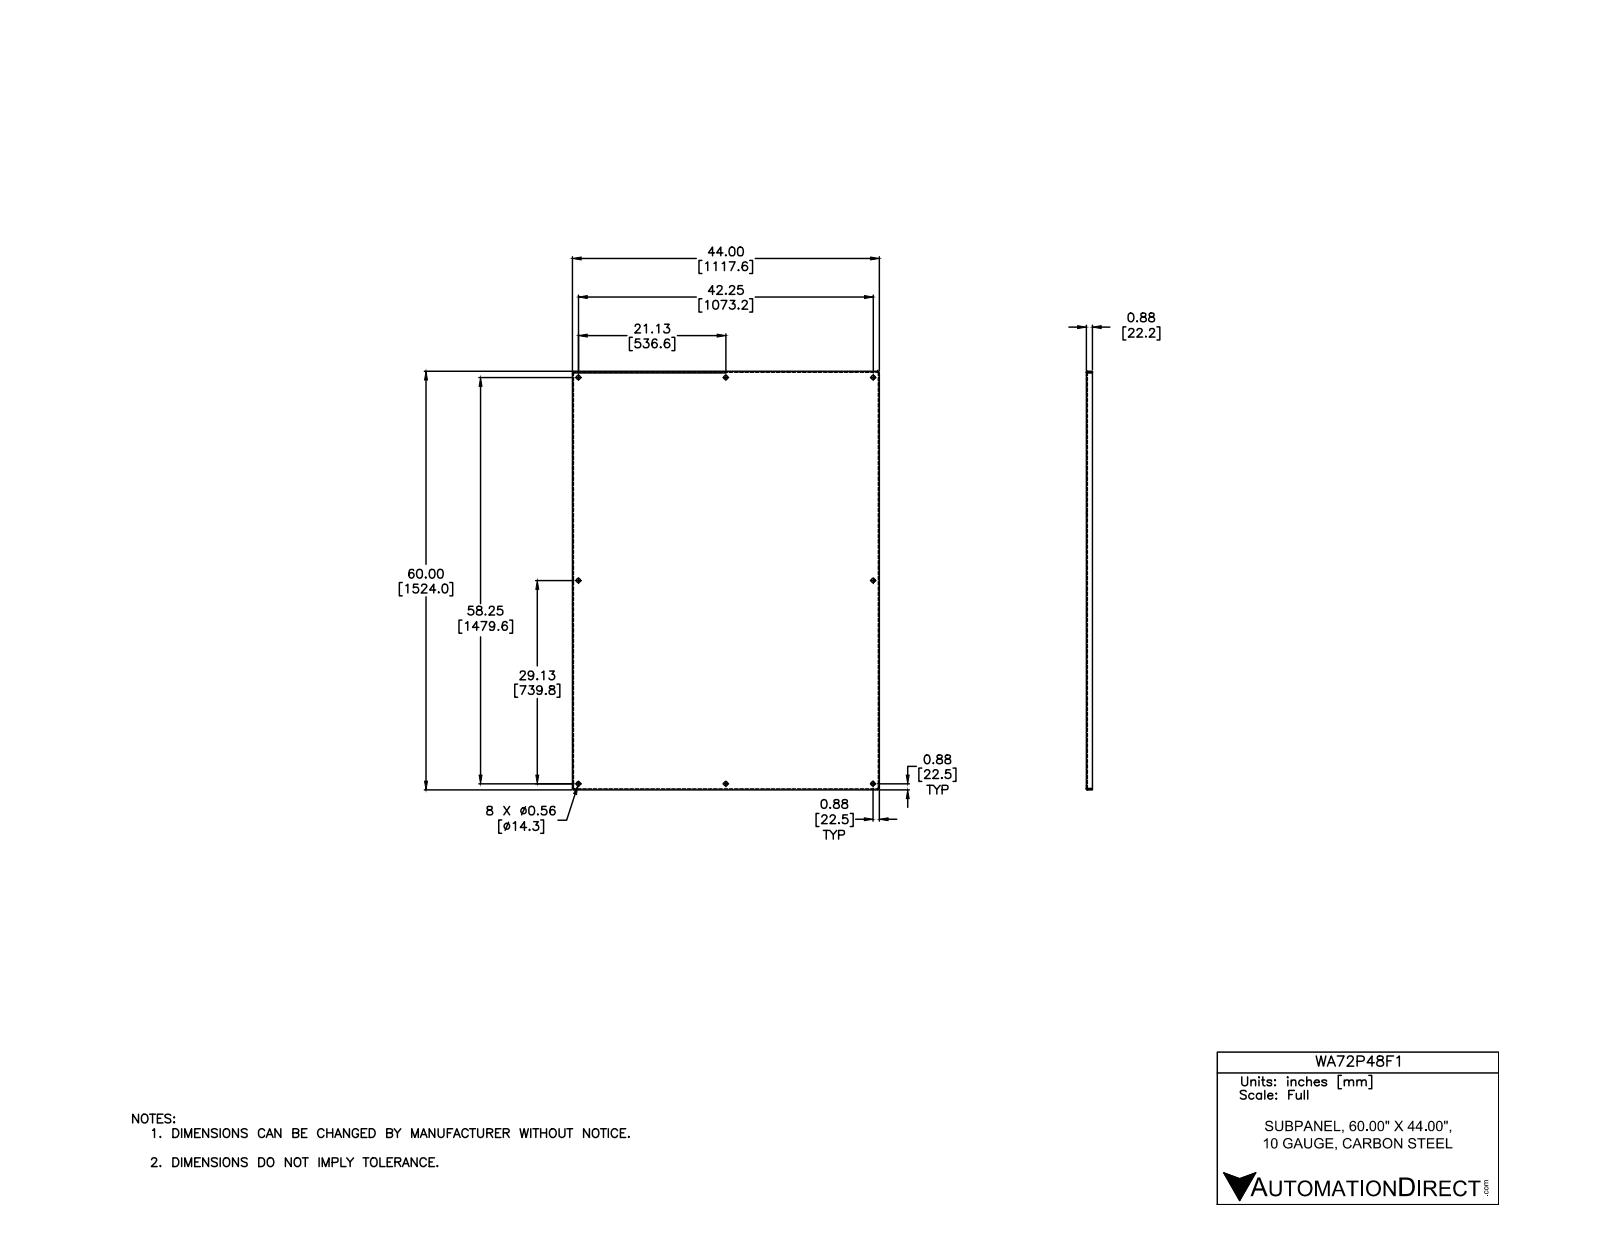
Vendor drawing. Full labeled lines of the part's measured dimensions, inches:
Part name (STEP PRODUCT): WA_P_F
STEP written by: Autodesk Inventor 2012 (AUTOMOTIVE_DESIGN)
Units: inches
Bodies: 1 solid, 46 faces (22 planar, 16 cylindrical, 8 other)
Overall size (bounding box): 60 × 44 × 0.875
Volume: 348 in³ · Surface area: 5 597 in²
Round holes (diameter × count): ⌀0.563 ×8
Partial cylindrical surfaces — rounded edges, fillets, slot ends (radius × count): R0.031 ×4, R0.156 ×4
Main face-to-face distances: 0.125, 0.125, 43.875, 59.875, 44, 43.75, 59.75, 60, 0.75, 0.875
Hole centre spacings: 21.125, 35.98, 42.25, 29.125, 29.125, 51.316, 51.317, 58.25
